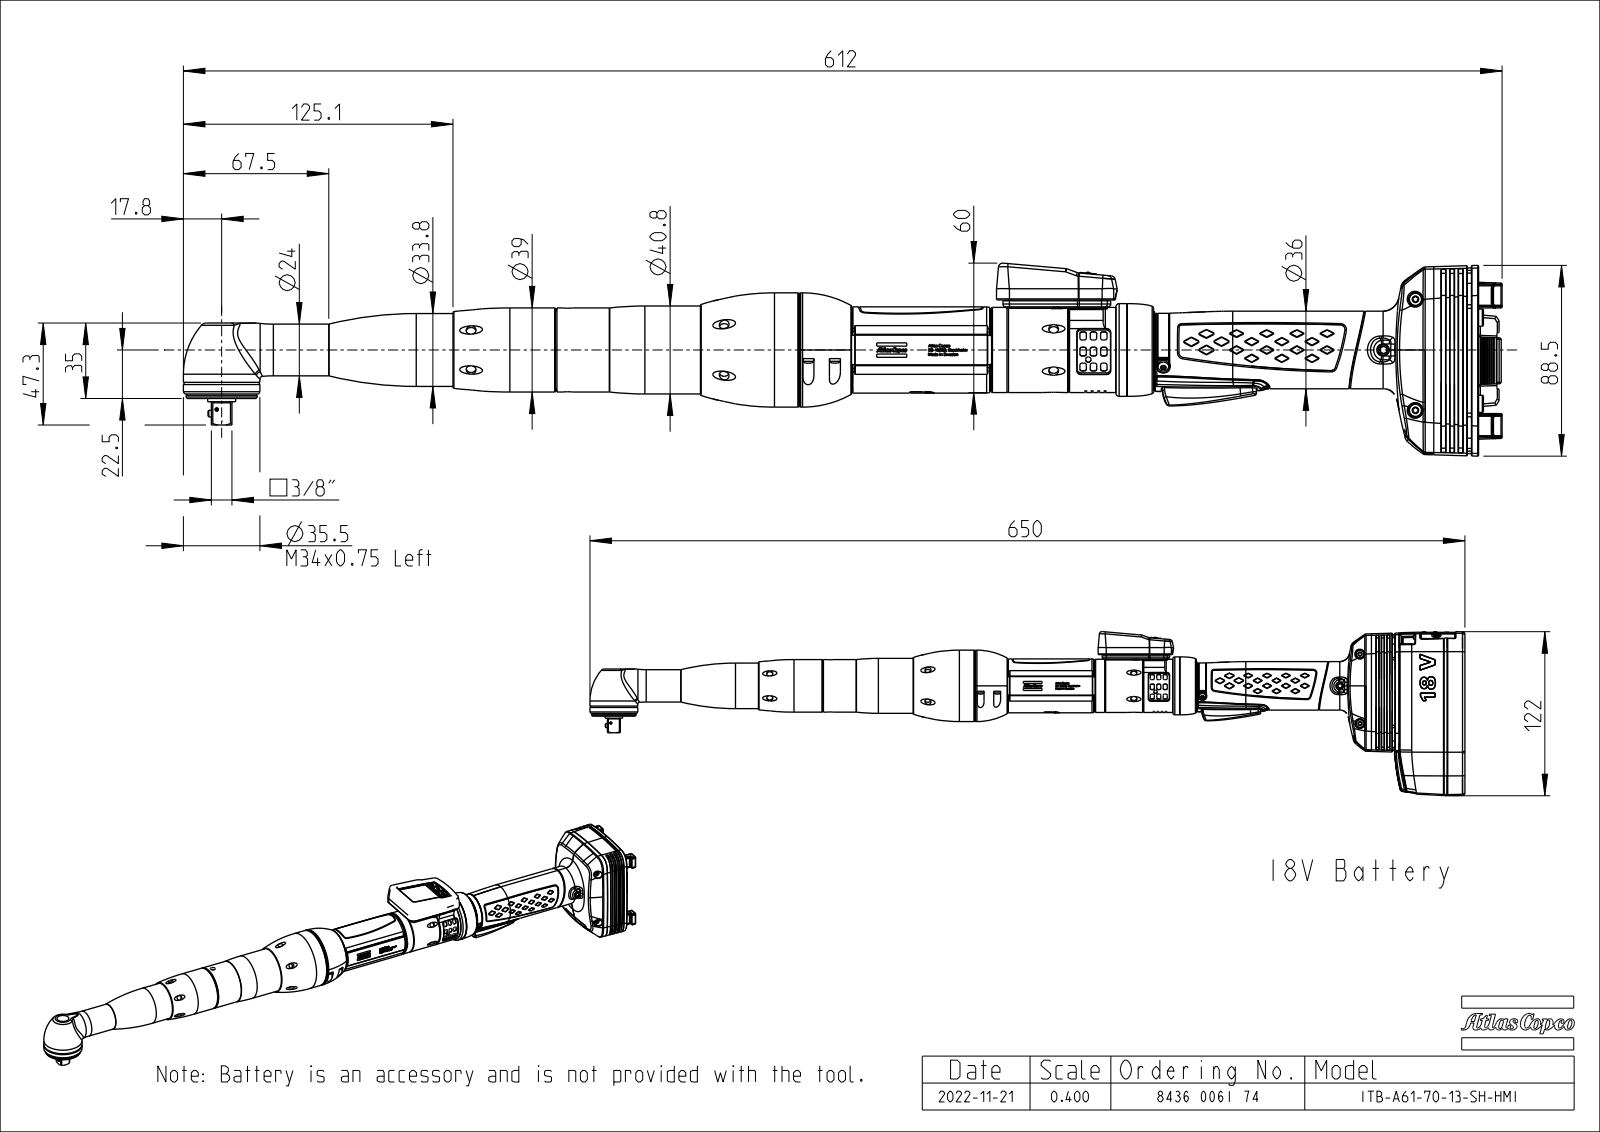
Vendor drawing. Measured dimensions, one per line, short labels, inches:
name: EXT_COMP_SW0002
written by: CREO PARAMETRIC BY PTC INC, 2020281 (CONFIG_CONTROL_DESIGN)
unit: in
bodies: 9 solids, 12207 faces (4628 planar, 2686 cylindrical, 4893 other)
size: 24.093 × 3.525 × 2.934
volume: 42.33 in³; area: 323.3 in²
holes: 15× ⌀0.177, 12× ⌀0.039, 9× ⌀0.126, 8× ⌀0.098, 4× ⌀0.081, 4× ⌀0.087, 4× ⌀0.106, 4× ⌀0.13, 4× ⌀0.169, 4× ⌀0.228, 4× ⌀0.256, 3× ⌀0.118
bosses: 3× ⌀0.138, 2× ⌀0.22, 2× ⌀0.118, 1× ⌀2.087, 1× ⌀1.988, 1× ⌀1.693, 1× ⌀1.606, 1× ⌀1.575
rounds: 533× R0.012, 250× R0.02, 226× R0.008, 126× R0.039, 110× R0.079, 36× R0.004, 29× R0.118, 28× R0.059
face distances: 0.098, 0.874, 0.199, 0.795, 0.079, 0.118, 0.909, 0.091, 0.697, 1.346
hole spacings: 0.118, 0.236, 0.453, 0.64, 0.75, 2.184, 2.294, 3.077
